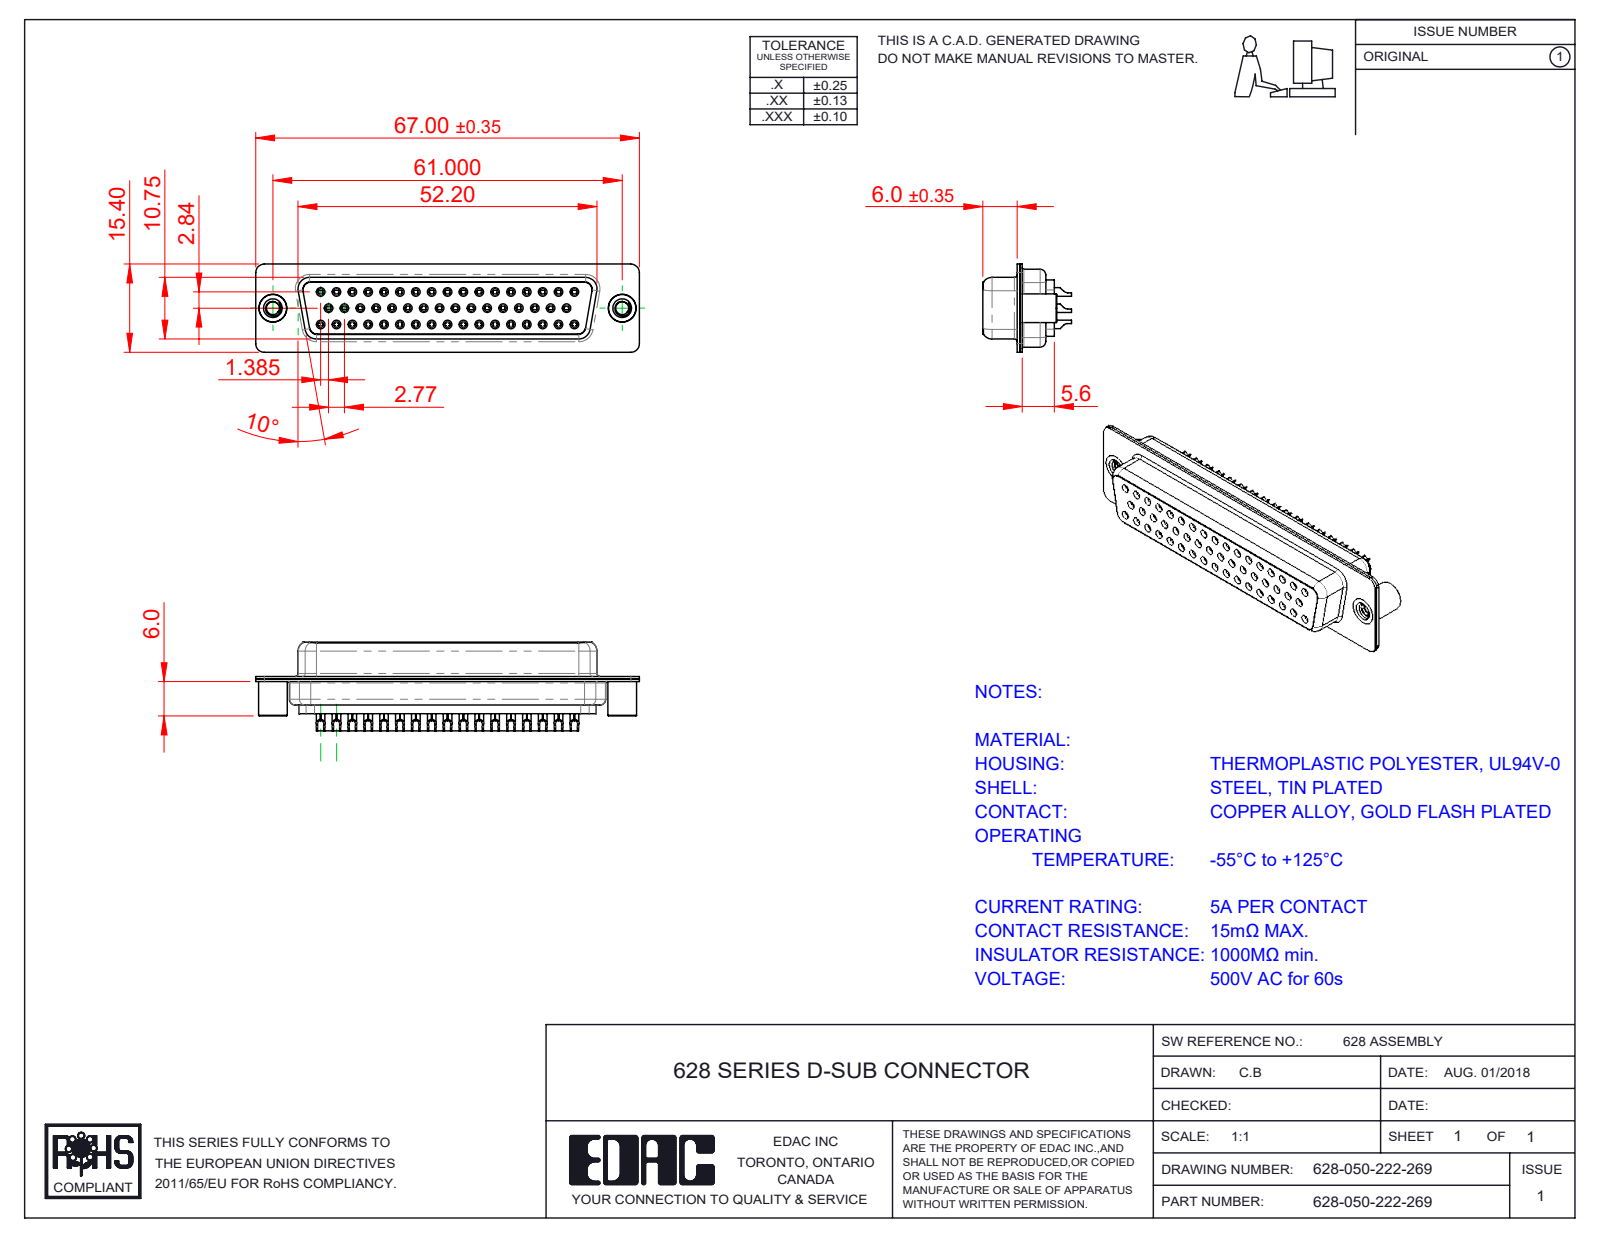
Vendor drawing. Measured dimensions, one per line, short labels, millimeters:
name: 628 Contact Row 3_22L; 628 Housing_50 LP; 628 4-40 Threaded Standoff BS; 628 Shell Front_50 Contacts (+4 more)
written by: SolidWorks 2020 (CONFIG_CONTROL_DESIGN)
unit: mm
bodies: 55 solids, 4751 faces (1117 planar, 1407 cylindrical, 2227 other)
size: 67 × 15.5 × 15.4
volume: 6 865 mm³; area: 15 804 mm²
holes: 50× ⌀0.8, 50× ⌀0.9, 50× ⌀1.1, 50× ⌀1.6, 17× ⌀1.7, 2× ⌀2.26, 2× ⌀4, 2× ⌀4.05, 2× ⌀4.85
bosses: 50× ⌀2, 50× ⌀1.5, 50× ⌀1.2, 2× ⌀5, 2× ⌀4.95, 2× ⌀4.8
rounds: 33× R0.28, 16× R1.5, 12× R2, 8× R1.35, 7× R1, 4× R0.25, 4× R0.5, 4× R0.6
face distances: 0.45, 0.4, 11.33, 1.87, 0.9, 6.5, 6.05, 6, 6.45, 10.3
hole spacings: 3.16, 2.77, 5.54, 8.31, 11.08, 13.85, 16.62, 19.39
